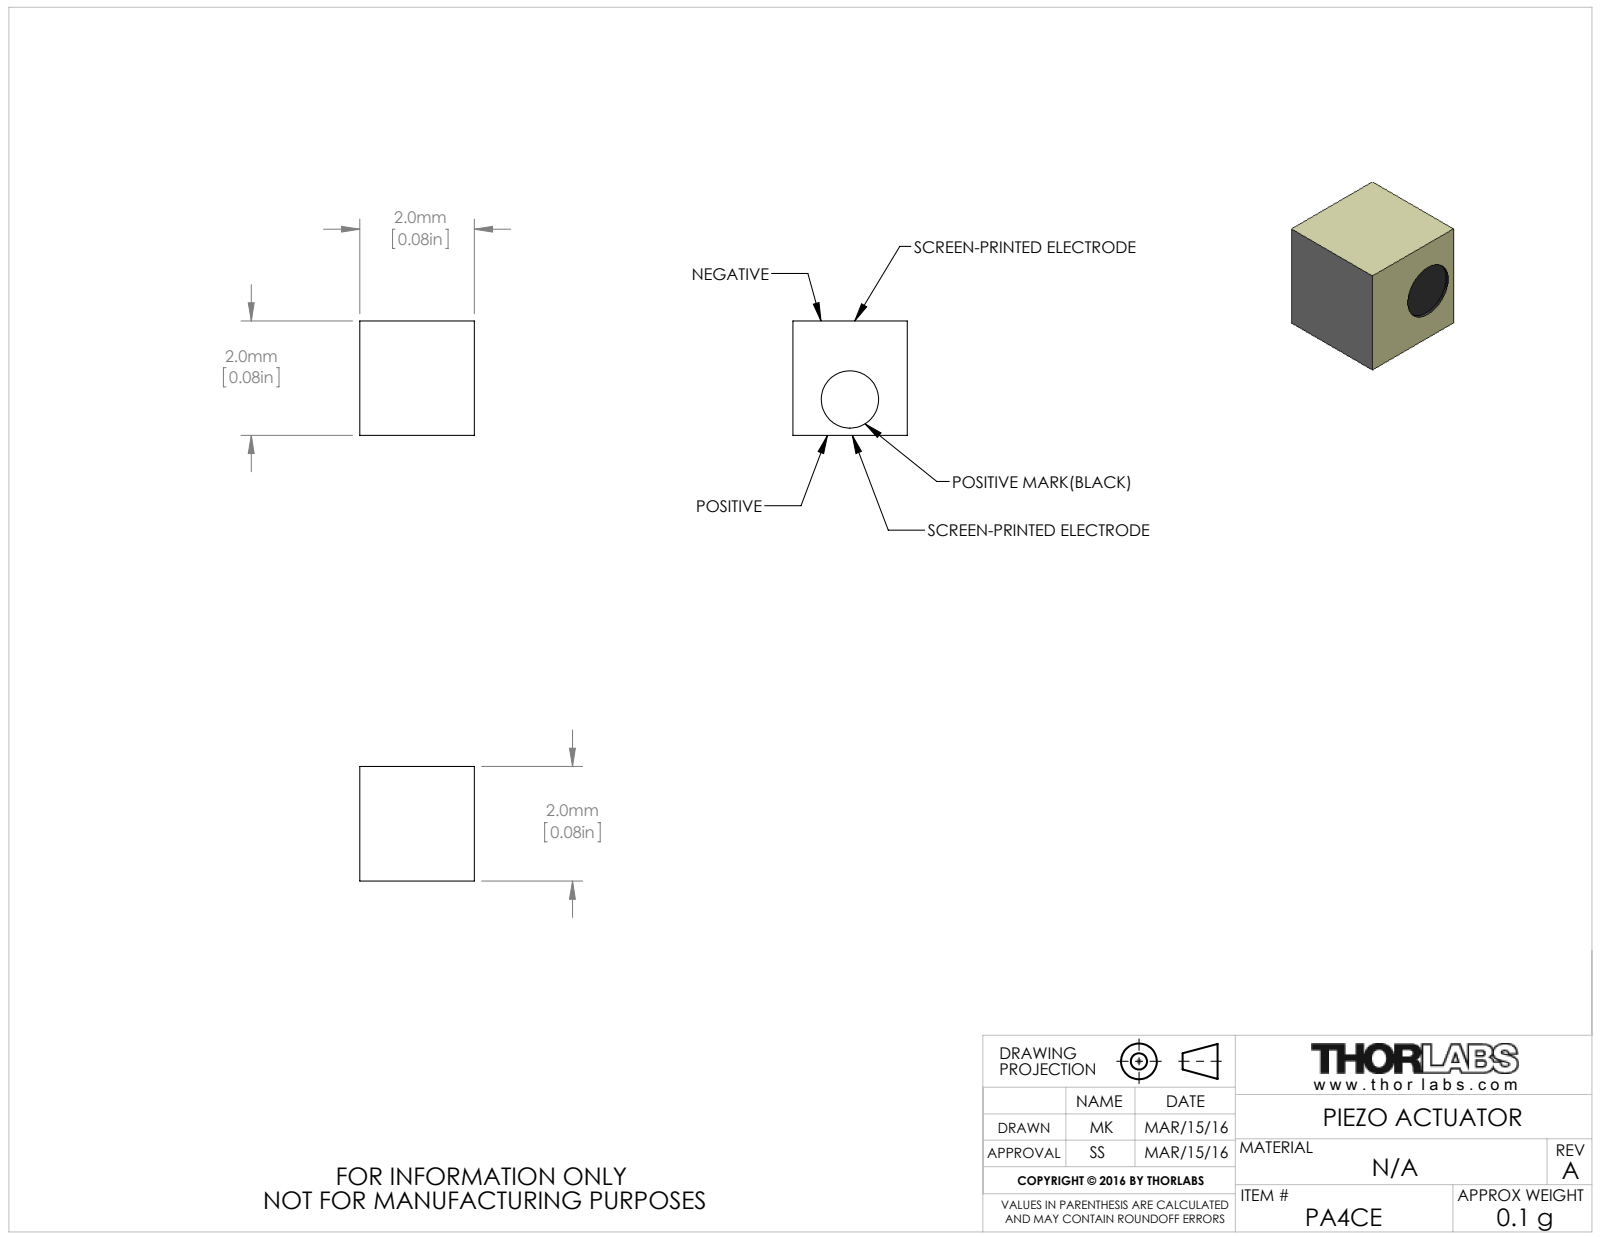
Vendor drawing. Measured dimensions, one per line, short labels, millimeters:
name: CTN002579
written by: SolidWorks 2014 (AUTOMOTIVE_DESIGN)
unit: mm
bodies: 1 solid, 9 faces (7 planar, 2 cylindrical, 0 other)
size: 2 × 2 × 2
volume: 8 mm³; area: 24 mm²
holes: 1× ⌀1
face distances: 2, 1.95
